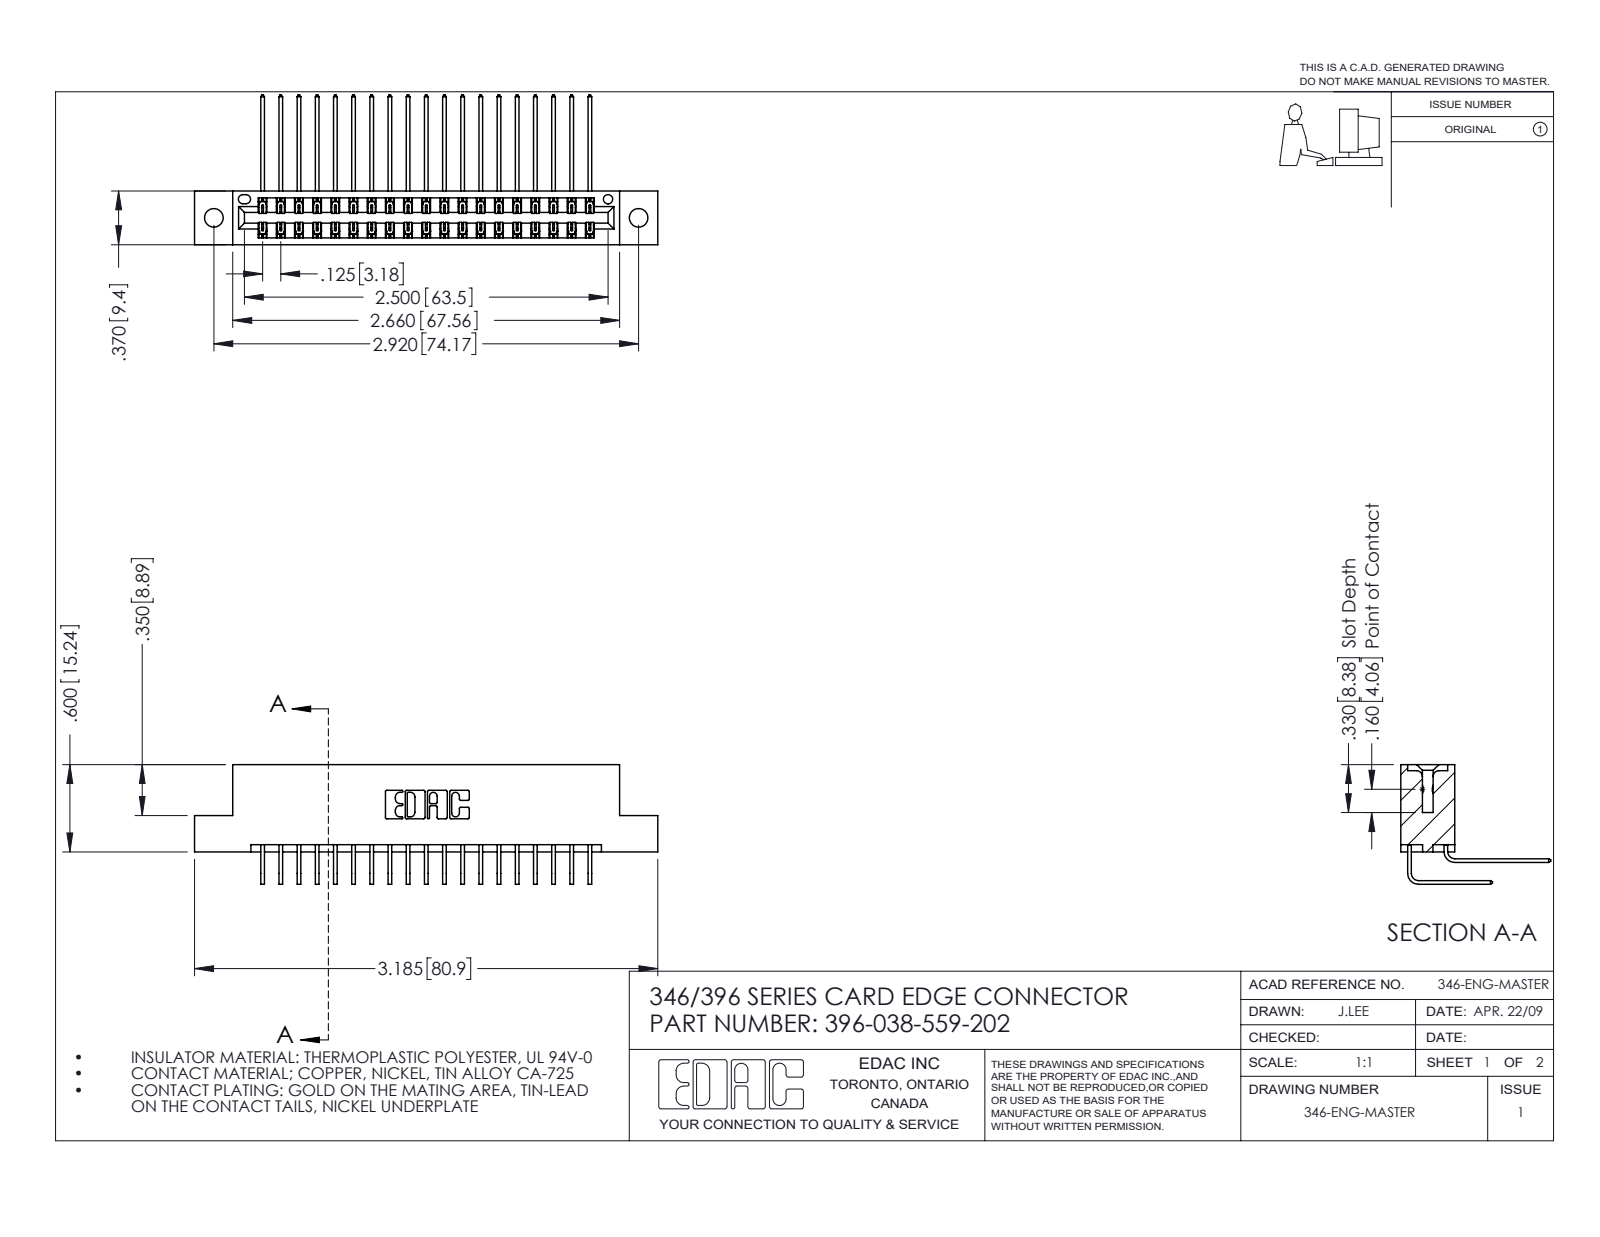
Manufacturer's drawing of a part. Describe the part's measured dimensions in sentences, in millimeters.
The part is named "346 Part_Flush Mounting Lugs - 0.128 Dia; 345-292-001_558 559 Tail - 1; 396-038-559-202; 345-292-001_559 Tail - 2". Its 3-D file was written by "SolidWorks 2016 (CONFIG_CONTROL_DESIGN)". It is 39 solids with 2174 faces: 1482 planar, 692 cylindrical and 0 other. Overall it measures 80.9 by 26.2 by 20.9 millimeters. Its volume is 7 900 cubic millimeters and its surface area 11 270 square millimeters. Round holes: 2 of diameter 3.3, 1 of diameter 1.6. Partial cylindrical surfaces (rounded edges, fillets, slot ends): 57 of radius 0.2, 22 of radius 0.3, 6 of radius 0.2, 6 of radius 0.8, 3 of radius 0.7, 2 of radius 0.4, 2 of radius 0.6, 2 of radius 0.6. The main face-to-face distances are 1.2, 8.2, 6.4, 0.6, 9.4, 1.8, 7.6, 7, 3.8, 5.6. The hole center spacings are 6.2, 68.9, 74.2.
